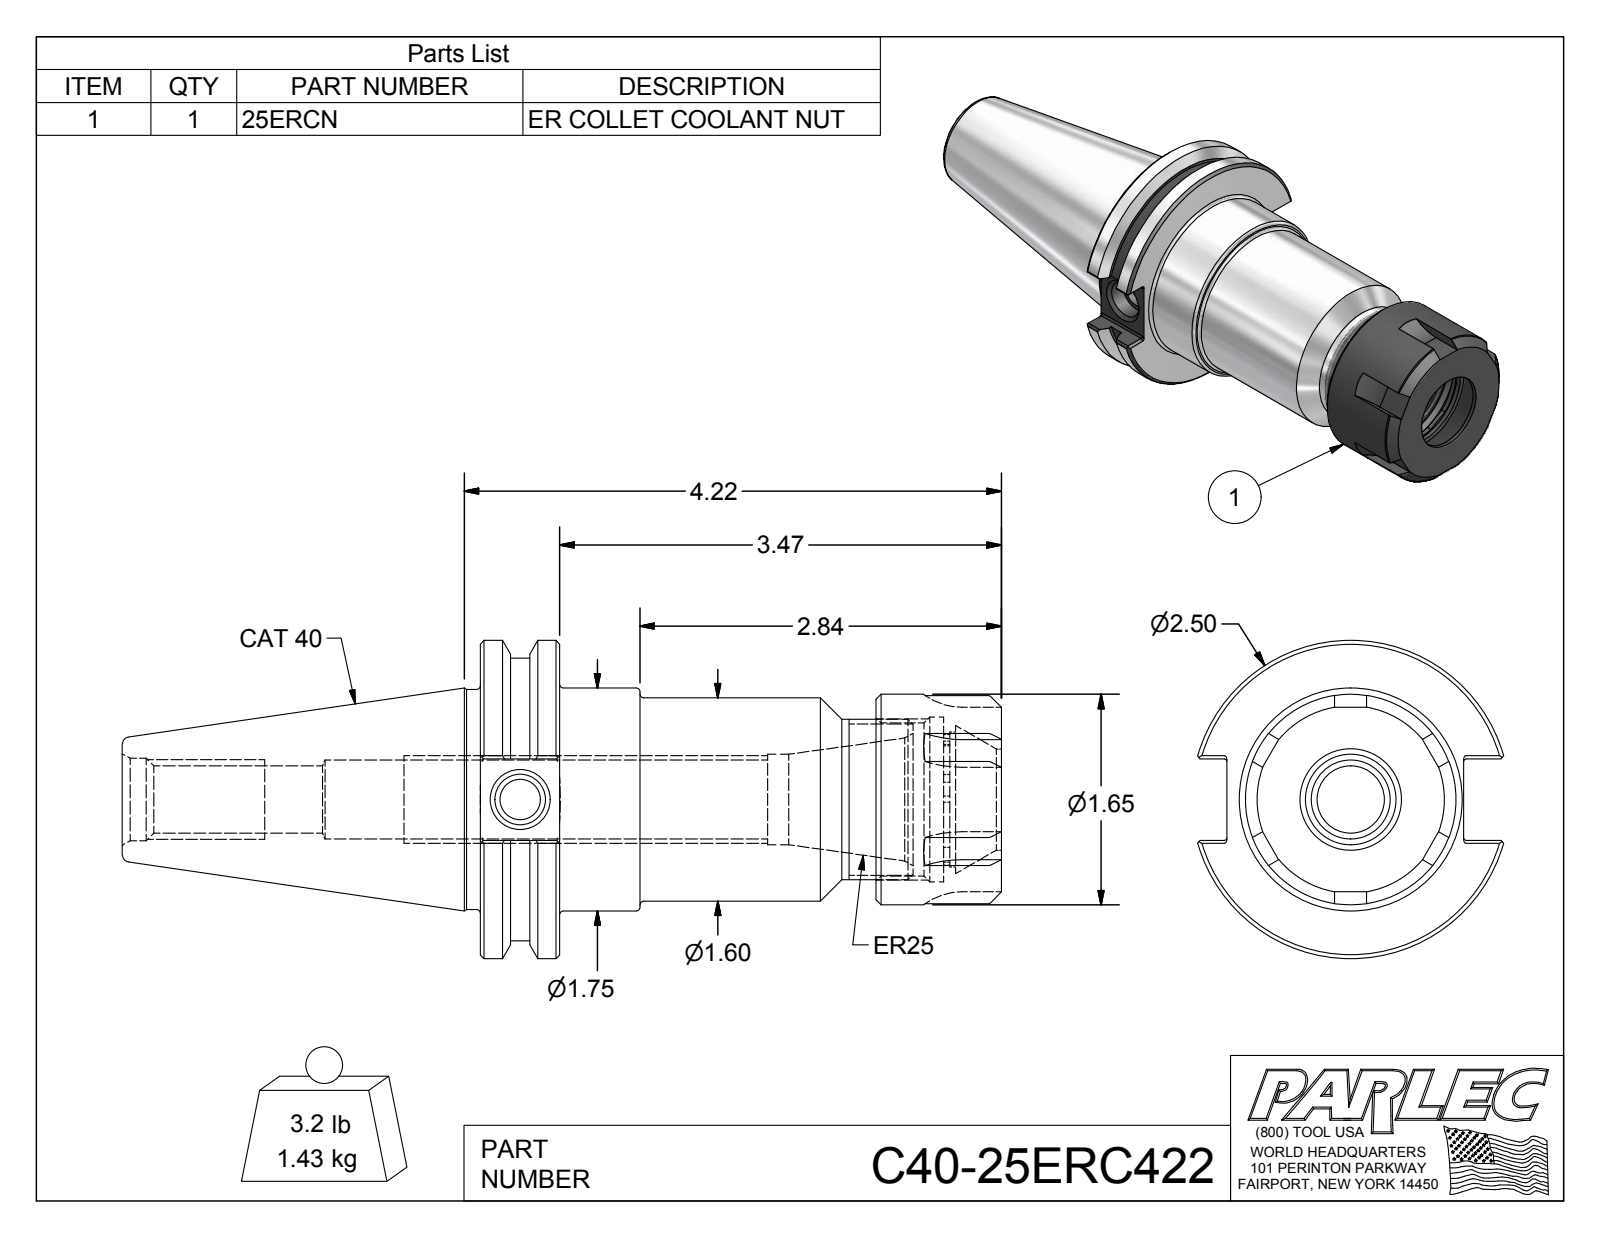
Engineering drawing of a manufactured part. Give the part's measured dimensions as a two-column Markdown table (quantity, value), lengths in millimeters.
| quantity | value |
| --- | --- |
| part name | C40-25ERC422; C40-25ER4-1; 25ERCN |
| STEP written by | Autodesk Inventor 2012 (AUTOMOTIVE_DESIGN) |
| units | millimeters |
| bodies | 2 solids, 145 faces (61 planar, 44 cylindrical, 40 other) |
| overall size | 175.5 × 63.5 × 61 |
| volume | 183 700 mm³ |
| surface area | 40 340 mm² |
| round holes (diameter × count) | 8 × 1, 10.1 × 1, 13.4 × 1, 15.7 × 1, 16.5 × 1, 18 × 1, 20.2 × 1, 26.8 × 1, 30.5 × 1, 32.9 × 1 |
| round bosses / shafts (diameter × count) | 63.5 × 1, 56.4 × 1, 44.5 × 1, 43.9 × 1, 42 × 1, 40.5 × 1, 32 × 1 |
| partial cylindrical surfaces (radius × count) | 0.5 × 12, 12.7 × 6, 12 × 1, 13.1 × 1 |
| main face-to-face distances | 15.9, 104, 88.1, 79, 63.1, 25, 92.5, 76.6, 13.5, 11.5 |
